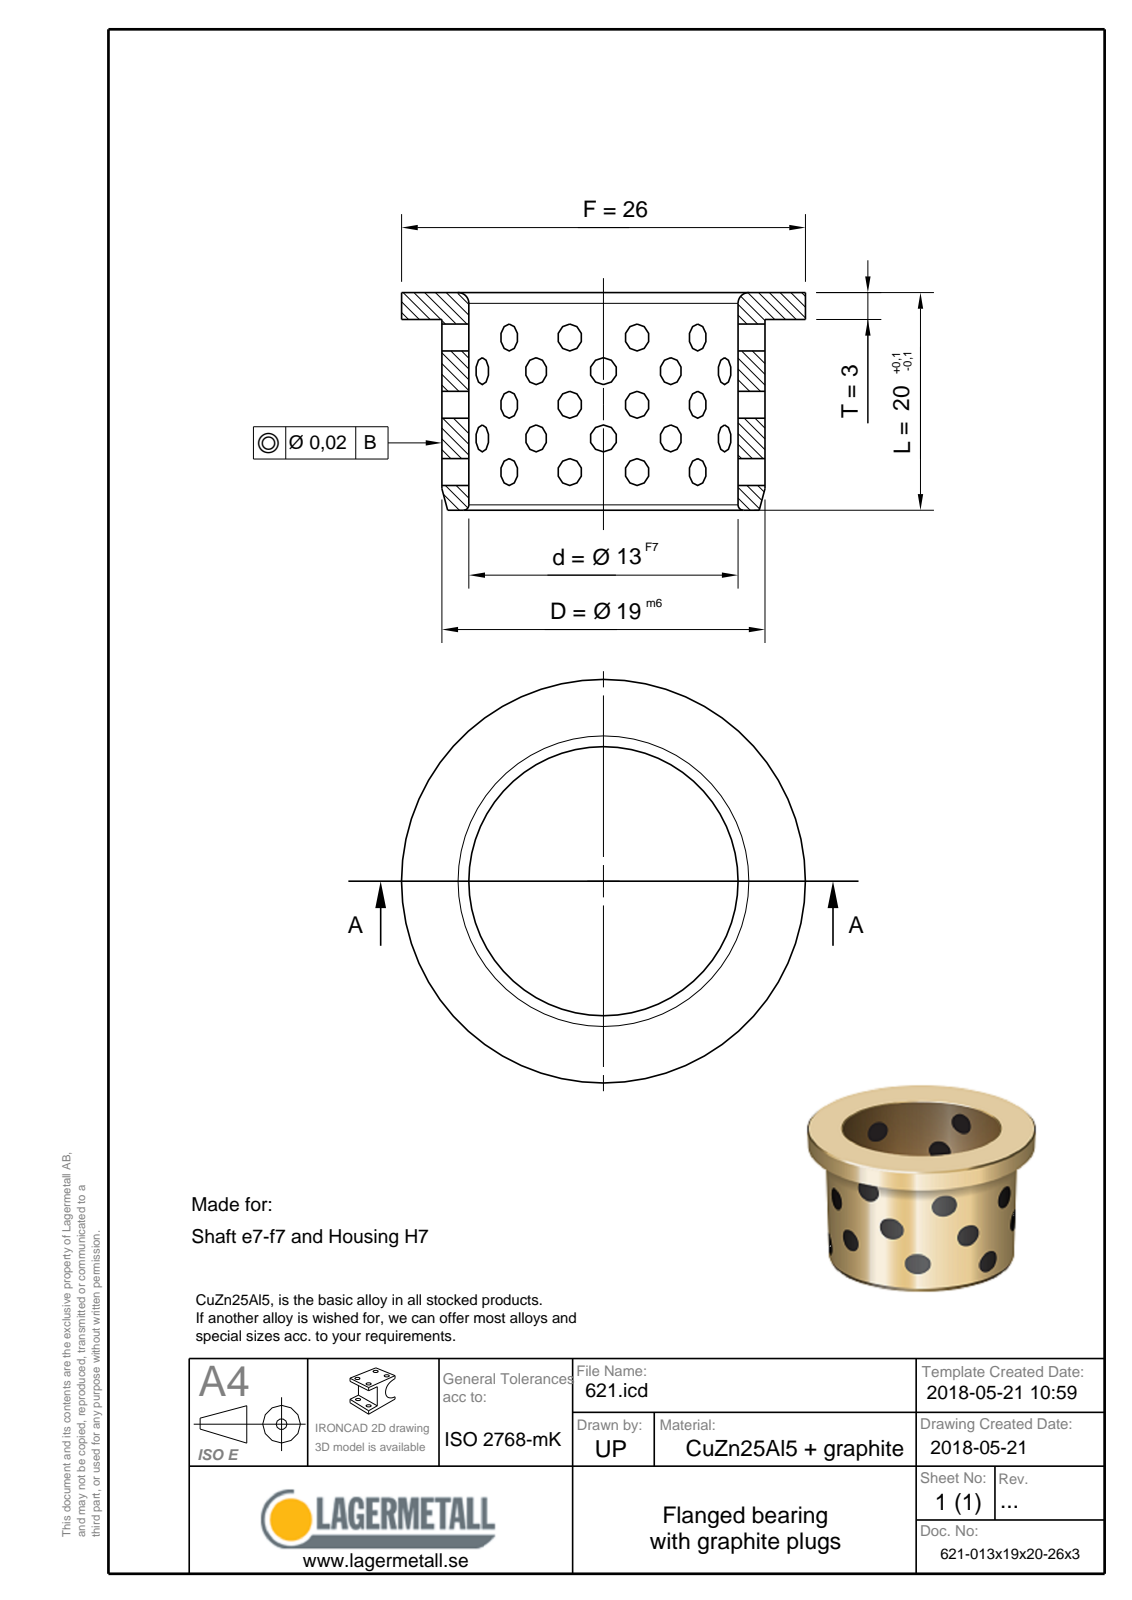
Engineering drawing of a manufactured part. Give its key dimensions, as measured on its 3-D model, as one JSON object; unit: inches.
{"part_name": "621-013x19x20-26x3", "step_written_by": "Spatial InterOp 3D (CONFIG_CONTROL_DESIGN)", "units": "inches", "bodies": {"solids": 1, "faces": 9, "planar": 3, "cylindrical": 3, "other": 3}, "overall_size": [1.024, 1.024, 0.787], "volume_in3": 0.224, "surface_area_in2": 4.311, "round_holes": [[0.512, 1]], "round_bosses_or_shafts": [[1.024, 1], [0.748, 1]], "face_to_face_distances": [0.118, 0.669, 0.787]}
